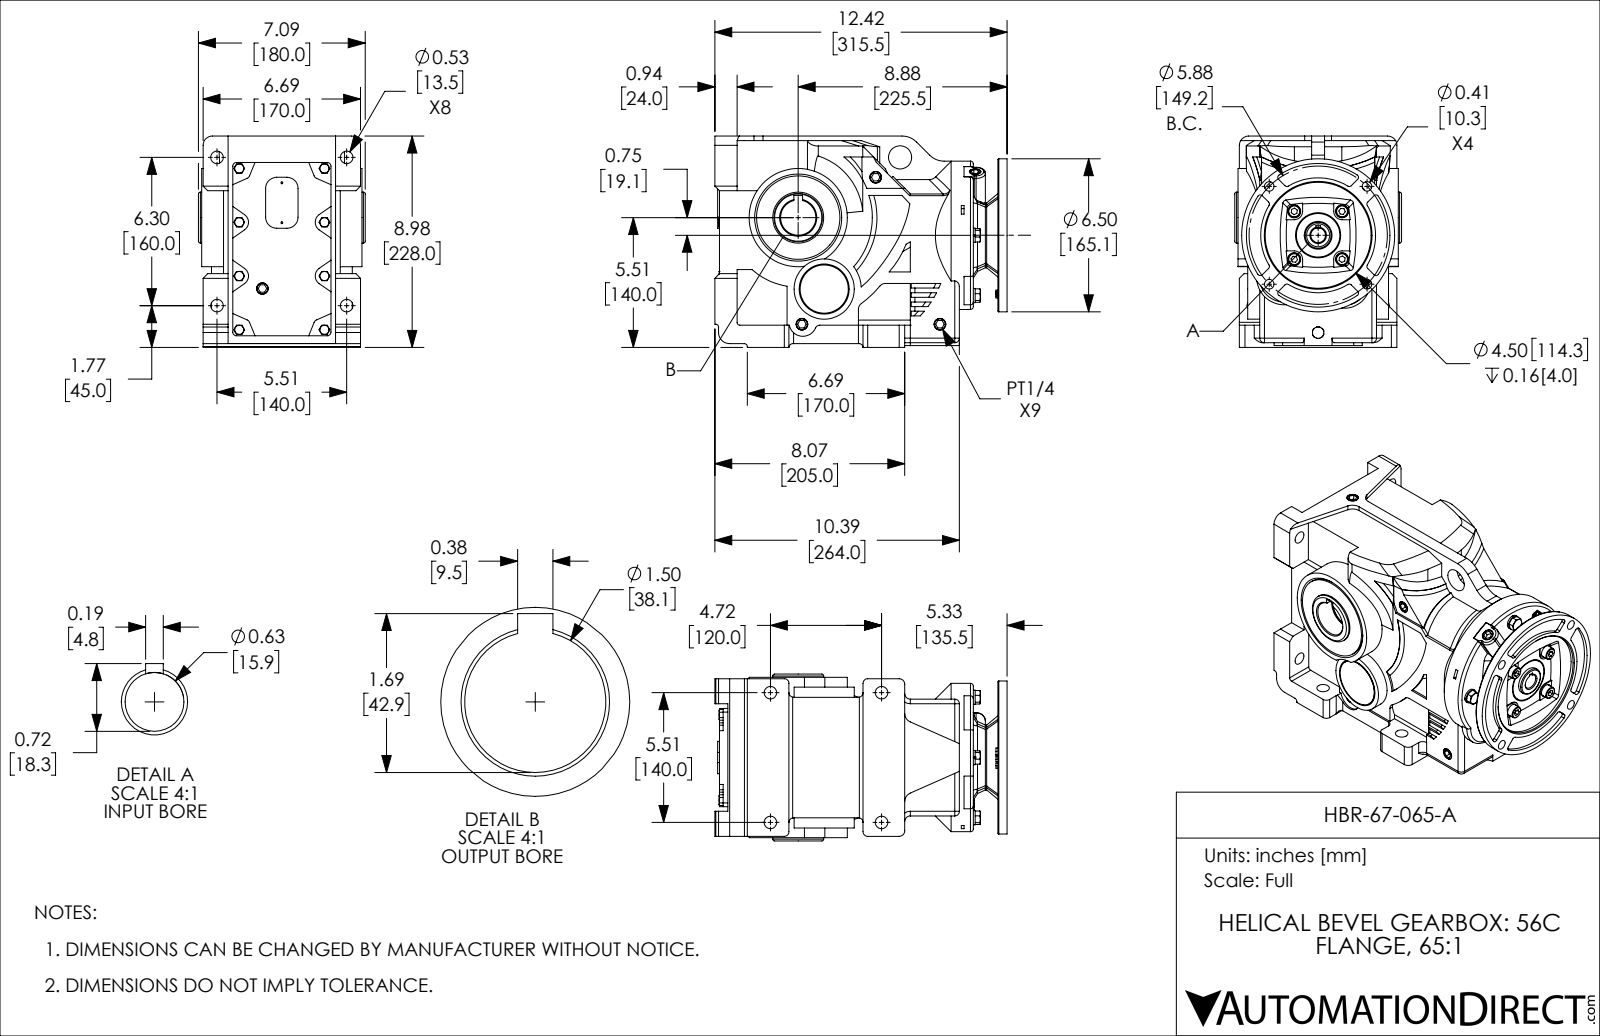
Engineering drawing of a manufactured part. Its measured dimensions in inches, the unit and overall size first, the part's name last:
Units: inches
Overall size (bounding box): 12.421 × 8.976 × 7.087
Round holes (diameter × count): ⌀0.531 ×8, ⌀0.323 ×4, ⌀0.354 ×4, ⌀0.406 ×4, ⌀0.551 ×4, ⌀0.079 ×2, ⌀0.625 ×1, ⌀0.846 ×1, ⌀0.984 ×1, ⌀1.5 ×1, ⌀1.575 ×1, ⌀4.5 ×1
Round bosses / shafts (diameter × count): ⌀0.606 ×4, ⌀0.512 ×4, ⌀0.315 ×4, ⌀6.5 ×1, ⌀6.299 ×1, ⌀4.173 ×1, ⌀3.543 ×1, ⌀2.559 ×1
Partial cylindrical surfaces — rounded edges, fillets, slot ends (radius × count): R0.118 ×23, R0.197 ×20, R0.394 ×13, R0.079 ×9, R0.157 ×6, R0.472 ×5, R0.236 ×4, R0.354 ×4
Main face-to-face distances: 0.197, 0.079, 0.157, 0.945, 8.78, 0.059, 4.961, 11.831, 0.118, 0.591
Hole centre spacings: 1.848, 2.132, 1.5, 2.559, 2.937, 3.27, 3.27, 3.619
Volume: 473.6 in³ · Surface area: 628.4 in²
Bodies: 1 solid, 1106 faces (550 planar, 274 cylindrical, 282 other)
Part name (STEP PRODUCT): HBR-67-065-A
STEP written by: SolidWorks 2018 (AUTOMOTIVE_DESIGN)
